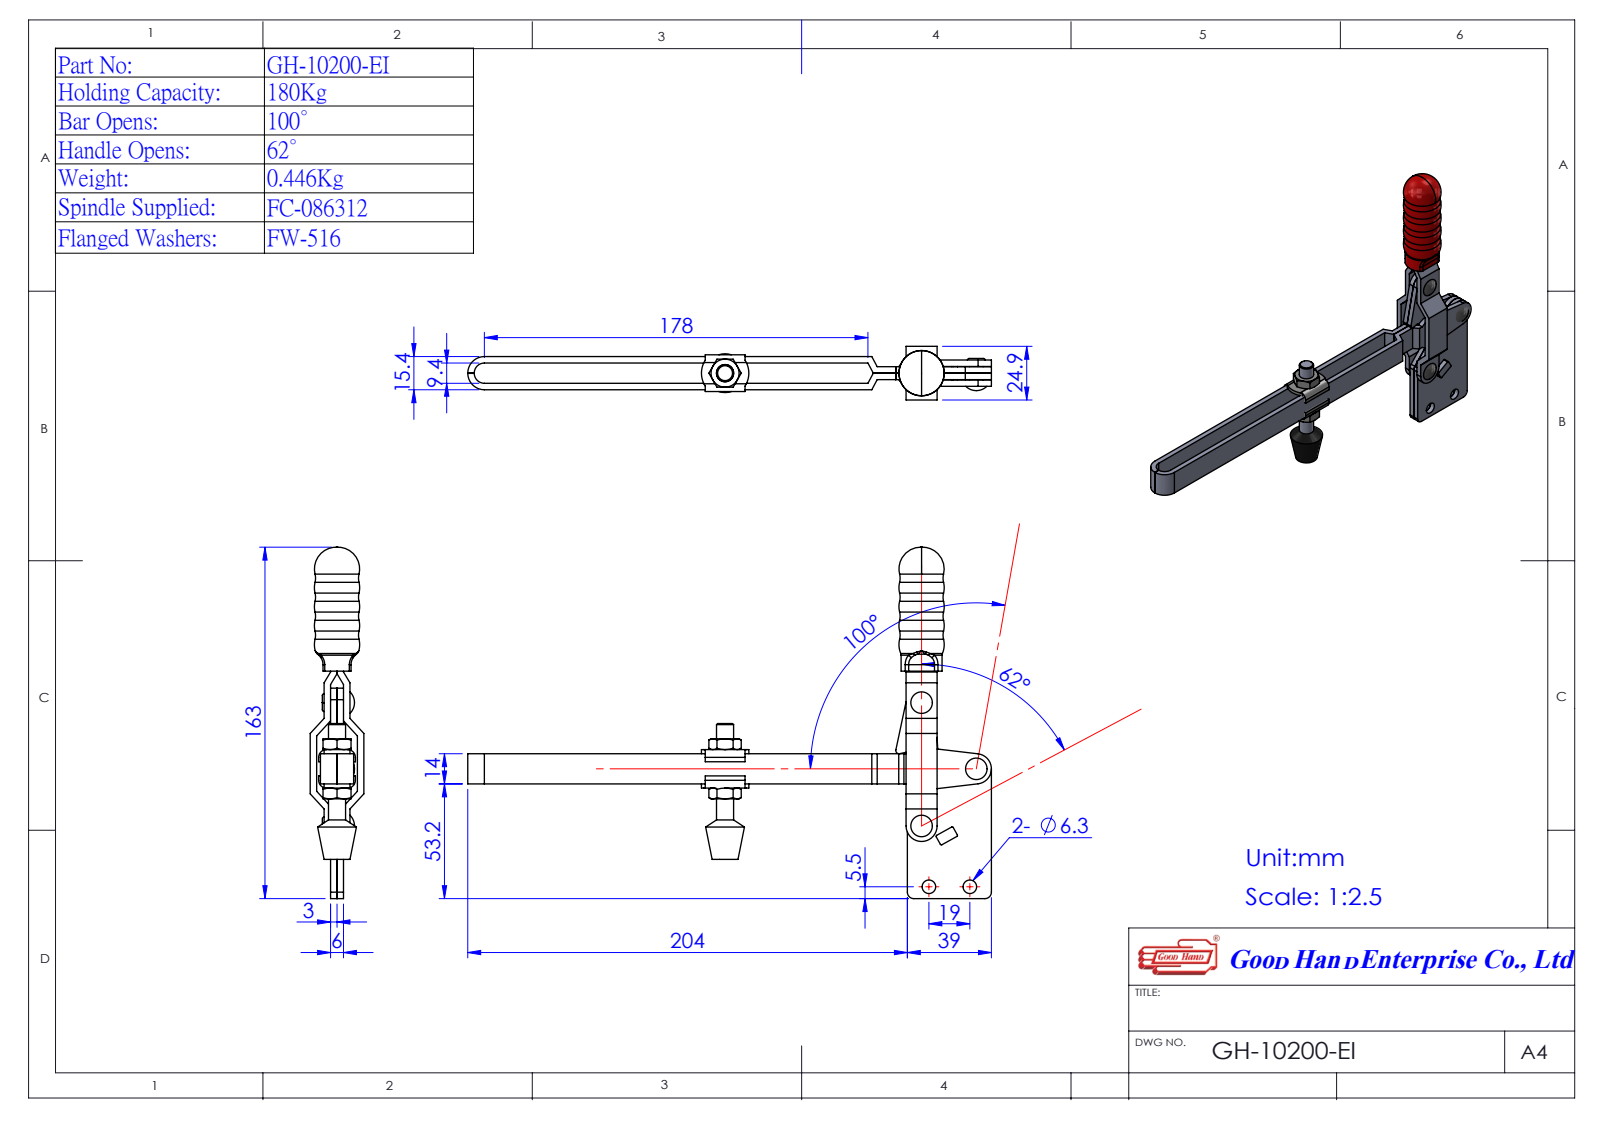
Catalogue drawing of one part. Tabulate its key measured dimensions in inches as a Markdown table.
| quantity | value |
| --- | --- |
| part name | Group2^GH-10200-EI(簡化)-1; Group4^GH-10200-EI(簡化)-1; Group5^GH-10200-EI(簡化)-1; 零件46^GH-10200-EI(簡化)-1 (+2 more) |
| STEP written by | SolidWorks 2016 (AUTOMOTIVE_DESIGN) |
| units | inches |
| bodies | 5 solids, 323 faces (136 planar, 93 cylindrical, 94 other) |
| overall size | 9.567 × 6.418 × 0.98 |
| volume | 4.309 in³ |
| surface area | 61.38 in² |
| round holes (diameter × count) | 0.197 × 4, 0.248 × 2 |
| round bosses / shafts (diameter × count) | 0.248 × 2, 0.312 × 1 |
| partial cylindrical surfaces (radius × count) | 0.02 × 4, 0.047 × 4, 0.079 × 4, 0.118 × 4, 0.142 × 4, 0.236 × 2, 0.266 × 2, 0.435 × 2 |
| main face-to-face distances | 0.118, 0.185, 0.303, 0.421, 0.067, 0.488, 0.236, 0.606, 0.37, 0.063 |
| hole center spacings | 0.748, 0.953, 1.044, 1.118, 1.209, 1.418, 1.445, 1.569 |
